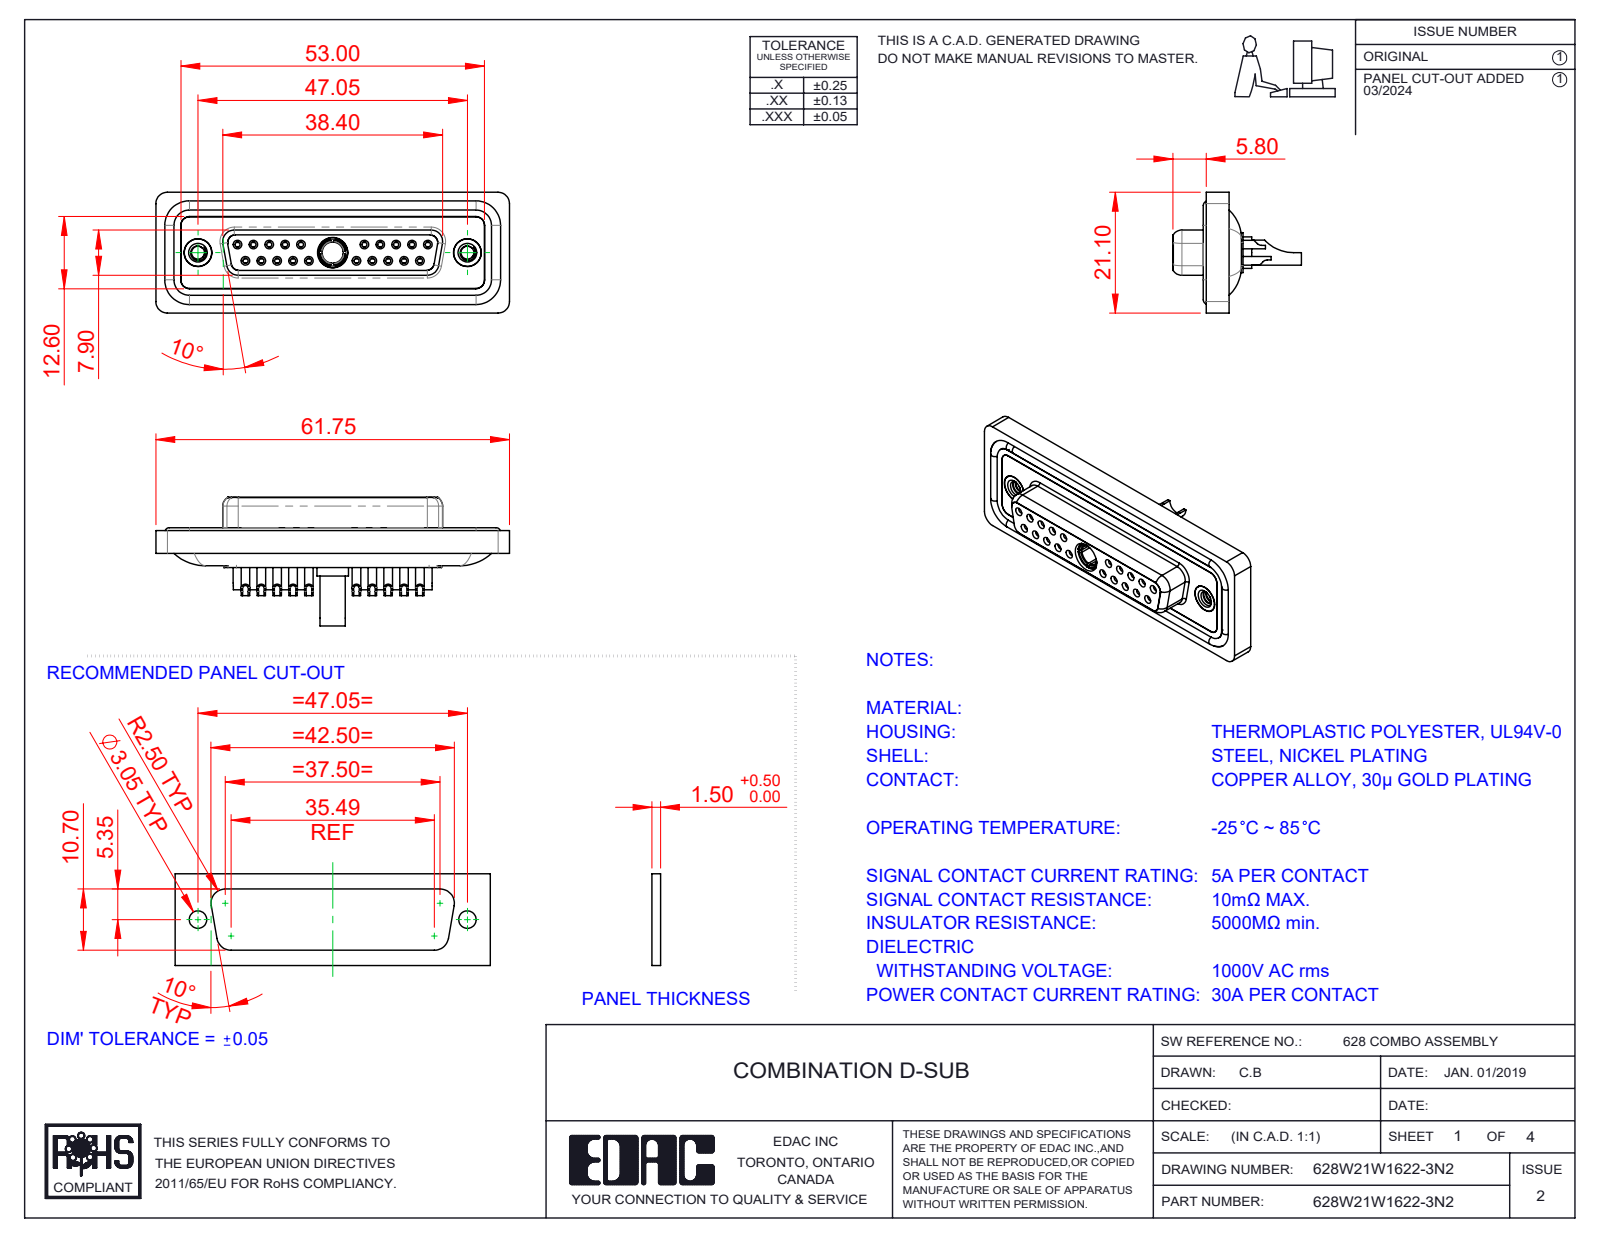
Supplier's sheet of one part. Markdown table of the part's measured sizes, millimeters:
| quantity | value |
| --- | --- |
| part name | 628Combo Contact Row 2_22; 628Combo Shell Front_25 Contacts; 628Combo Waterproof Housing_25 Contacts; 628Combo Contact Row 1_22 (+5 more) |
| STEP written by | SolidWorks 2023 (CONFIG_CONTROL_DESIGN) |
| units | millimeters |
| bodies | 29 solids, 1566 faces (477 planar, 634 cylindrical, 455 other) |
| overall size | 61.75 × 22.45 × 21.1 |
| volume | 8 439 mm³ |
| surface area | 14 320 mm² |
| round holes (diameter × count) | 0.9 × 20, 1 × 20, 1.1 × 20, 1.5 × 20, 2 × 20, 1.6 × 10, 1.7 × 10, 4.85 × 3, 2.26 × 2, 4 × 2, 4.05 × 2, 5 × 2 |
| round bosses / shafts (diameter × count) | 2.2 × 20, 1.6 × 14, 4.95 × 2, 4.8 × 2, 5.5 × 1, 5.2 × 1, 4.96 × 1, 4.75 × 1 |
| partial cylindrical surfaces (radius × count) | 1.5 × 22, 2 × 18, 1.35 × 8, 1.6 × 8, 1 × 6, 0.25 × 4, 0.5 × 4, 0.6 × 4 |
| main face-to-face distances | 0.4, 1.8, 7.45, 5.65, 6.6, 0.5, 1.6, 7.05, 2.9, 1.1 |
| hole center spacings | 3.16, 2.77, 5.54, 5.03, 8.31, 7.48, 16.62, 19.39 |
